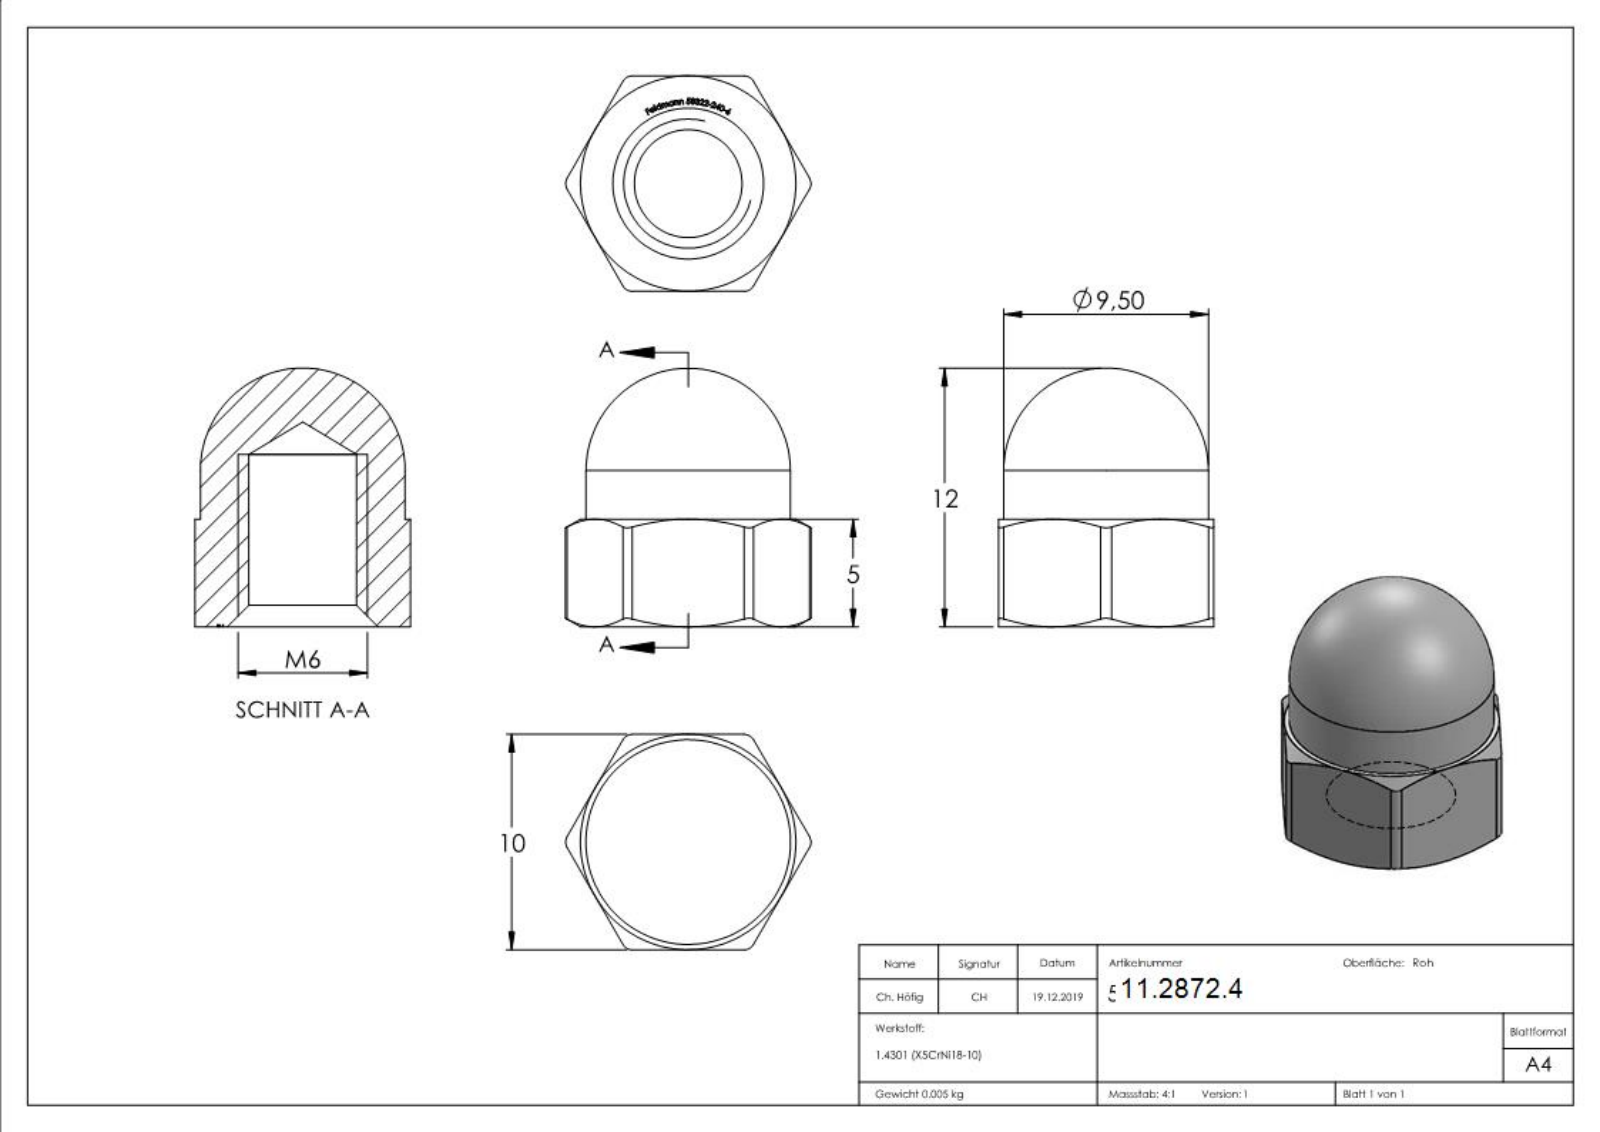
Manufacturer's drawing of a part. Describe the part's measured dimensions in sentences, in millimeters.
The part is named "58322-240-6". Its 3-D file was written by "SolidWorks 2015 (CONFIG_CONTROL_DESIGN)". It is 1 solid with 31 faces: 8 planar, 8 cylindrical and 15 other. Overall it measures 17 by 11.39 by 10 millimeters. Its volume is 639 cubic millimeters and its surface area 596 square millimeters. Round holes: 1 of diameter 5. Round bosses or shafts: 1 of diameter 9.5. Partial cylindrical surfaces (rounded edges, fillets, slot ends): 6 of radius 0.5. The main face-to-face distances are 10, 5.
